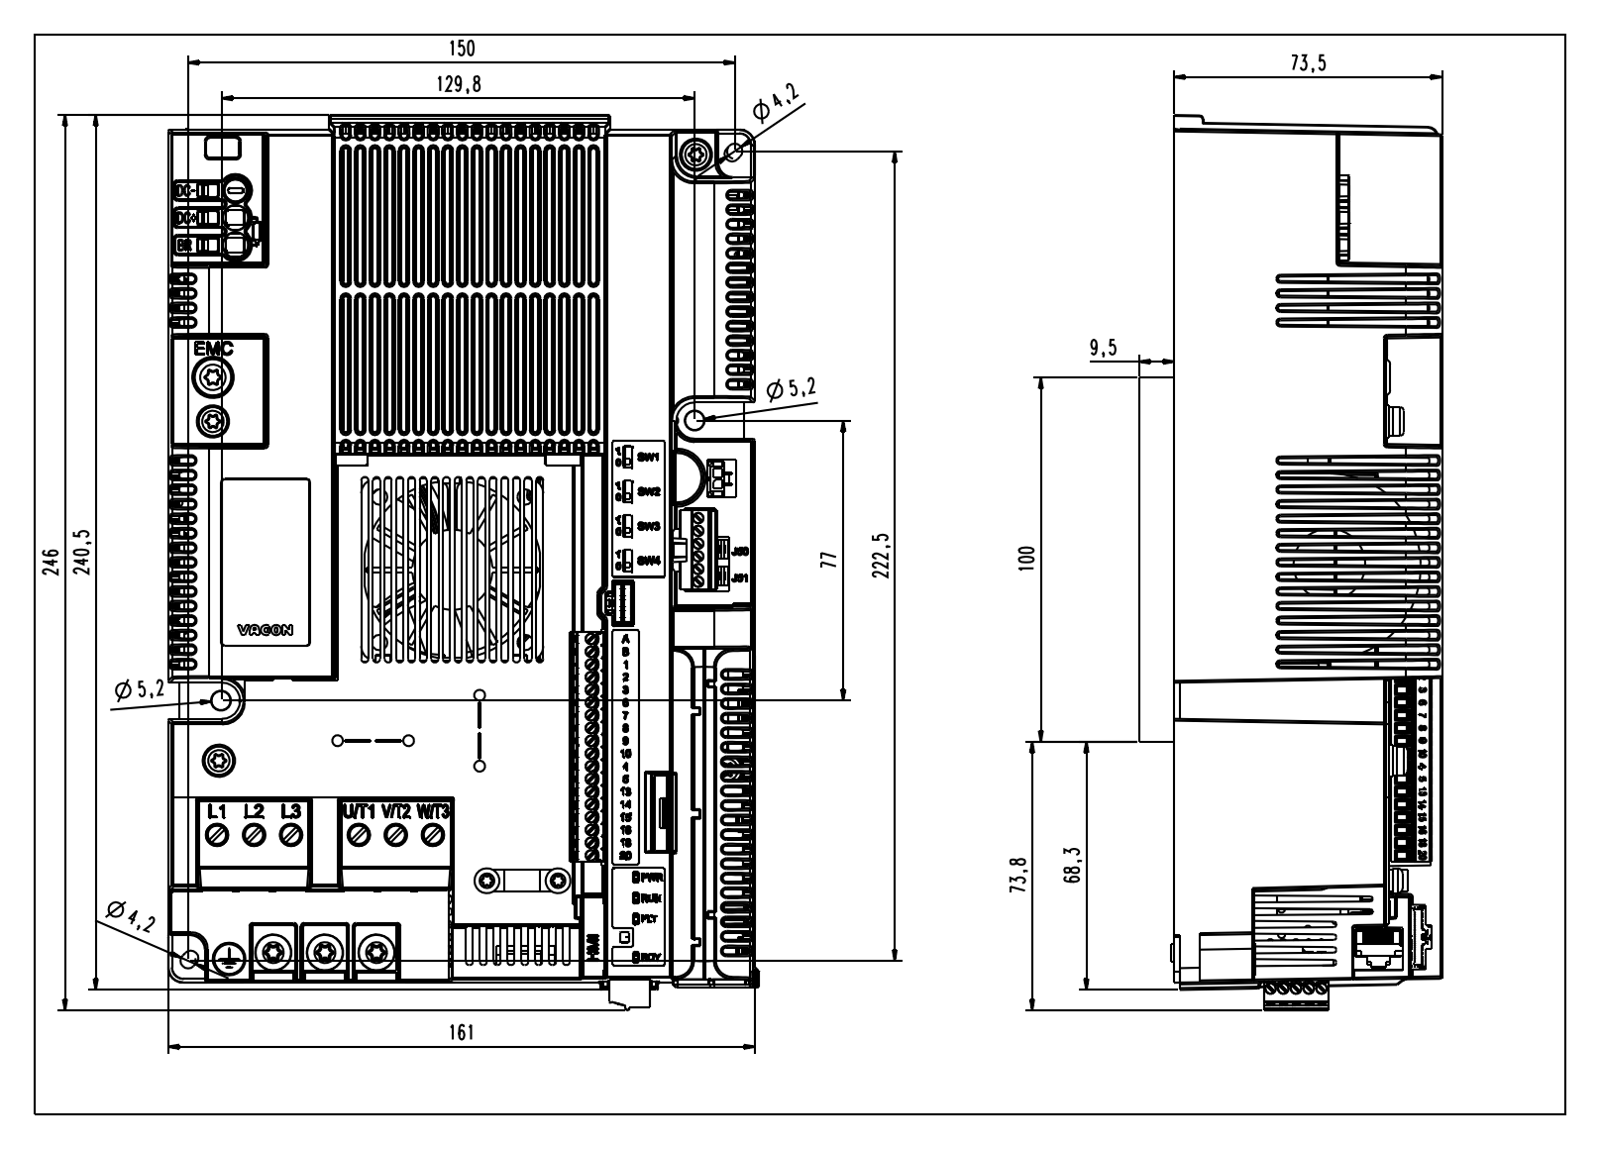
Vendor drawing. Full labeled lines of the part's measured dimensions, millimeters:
Part name (STEP PRODUCT): CAD-3D-VACON20X-MS3; CAD-3D-VACON20X-MS3.sldasm-Part-1_Standard; CAD-3D-VACON20X-MS3.sldasm-Part-2_Standard; CAD-3D-VACON20X-MS3.sldasm-Part-3_Standard (+8 more)
STEP written by: SolidWorks 2007 (CONFIG_CONTROL_DESIGN)
Units: millimetres
Bodies: 58 solids, 10921 faces (4276 planar, 2929 cylindrical, 3716 other)
Overall size (bounding box): 240.47 × 162.08 × 83.4
Volume: 584 387 mm³ · Surface area: 480 999 mm²
Round holes (diameter × count): ⌀3 ×11, ⌀4 ×8, ⌀2.9 ×6, ⌀1 ×4, ⌀6.4 ×4, ⌀1.6 ×3, ⌀3.2 ×3, ⌀4.2 ×3, ⌀5 ×3, ⌀6 ×3, ⌀3.4 ×2, ⌀3.5 ×2
Round bosses / shafts (diameter × count): ⌀2.8 ×6, ⌀1 ×6, ⌀9 ×5, ⌀2 ×5, ⌀1.2 ×5, ⌀3.3 ×3, ⌀2.2 ×3, ⌀0.46 ×3
Partial cylindrical surfaces — rounded edges, fillets, slot ends (radius × count): R0.5 ×795, R0.25 ×297, R0.3 ×103, R1 ×81, R0.65 ×74, R0.2 ×70, R0.6 ×66, R0.1 ×45
Main face-to-face distances: 2.5, 1.5, 11, 9.5, 1, 12, 14.5, 9.7, 11.2, 68.5
Hole centre spacings: 3.5, 7, 10.5, 14, 14.17, 73.05, 77.26, 114
